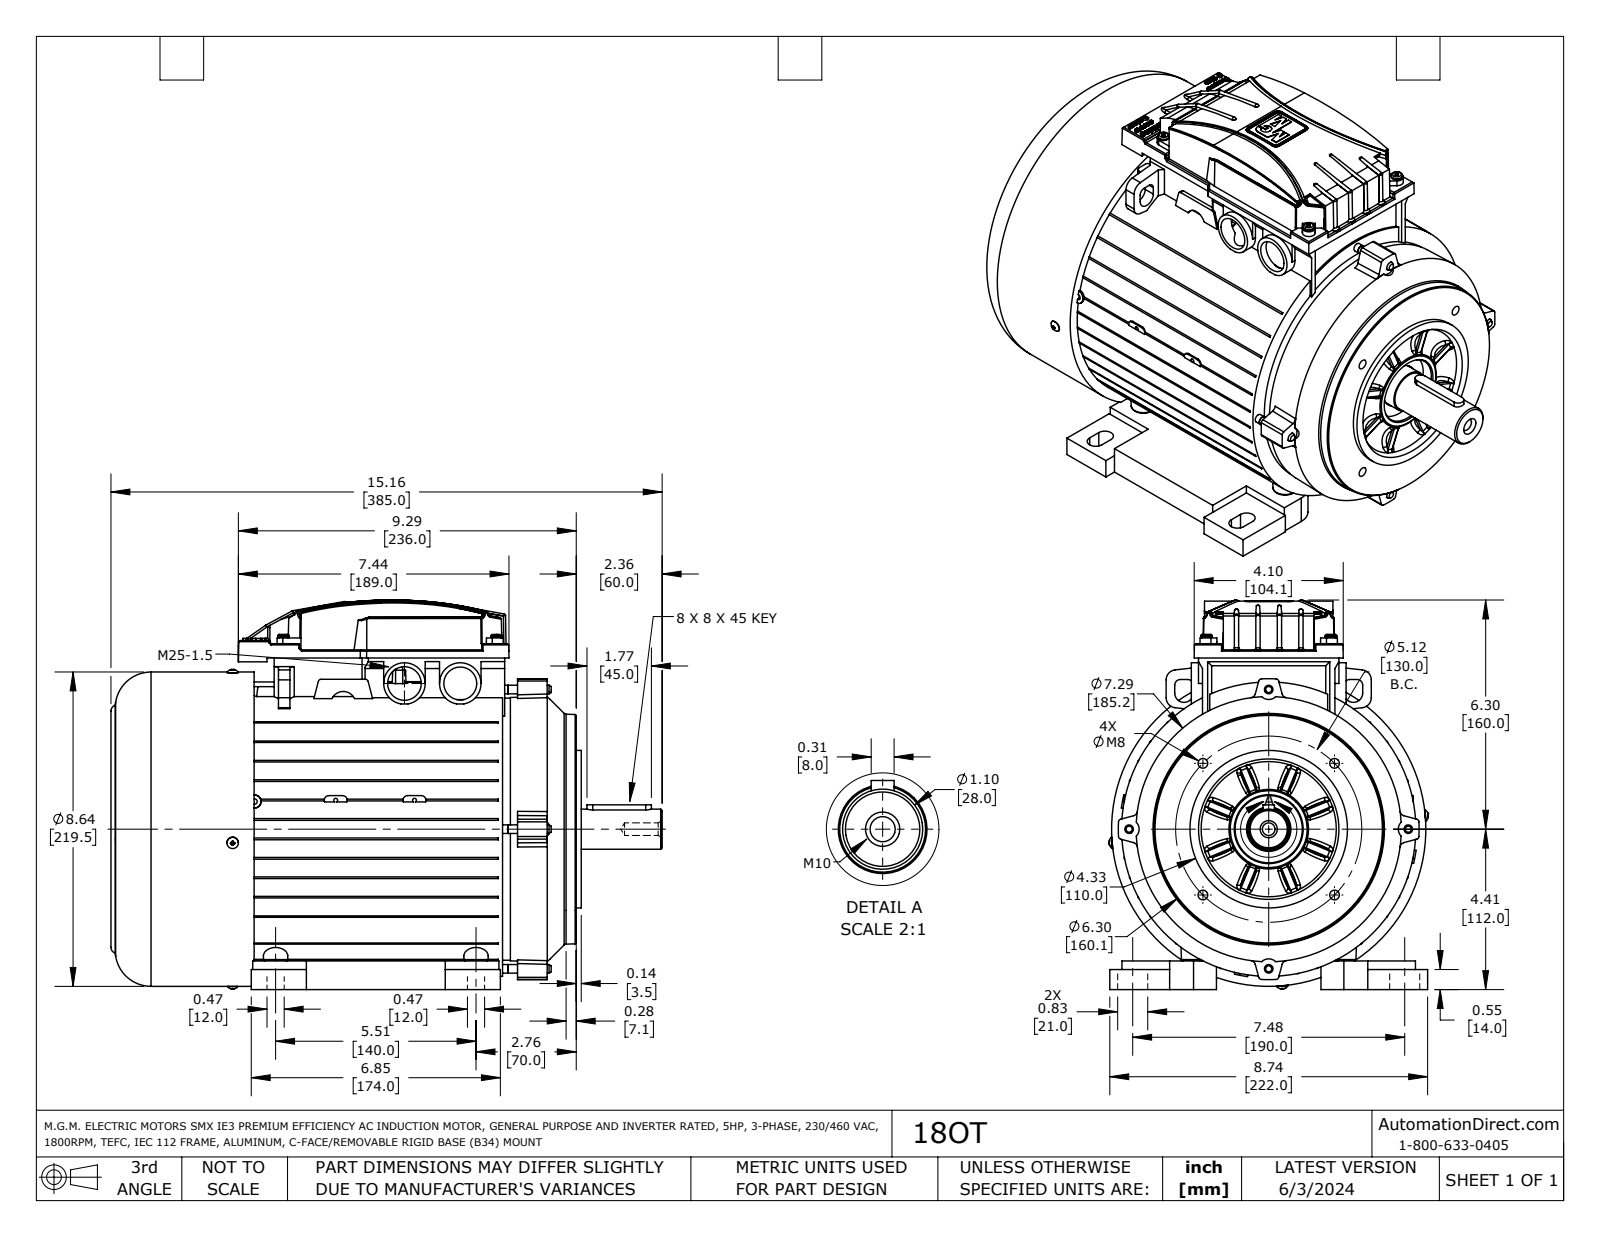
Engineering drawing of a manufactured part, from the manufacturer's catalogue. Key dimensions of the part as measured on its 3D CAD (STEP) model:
Part name (STEP PRODUCT): 18OT
STEP written by: SolidWorks 2021 (AUTOMOTIVE_DESIGN)
Units: inches
Bodies: 16 solids, 3525 faces (1703 planar, 684 cylindrical, 1138 other)
Overall size (bounding box): 15.157 × 10.709 × 8.78
Volume: 651.5 in³ · Surface area: 993.3 in²
Round holes (diameter × count): ⌀0.098 ×5, ⌀0.13 ×5, ⌀0.177 ×4, ⌀0.197 ×4, ⌀0.268 ×4, ⌀0.335 ×4, ⌀0.531 ×4, ⌀0.106 ×2, ⌀0.165 ×2, ⌀0.346 ×1, ⌀0.906 ×1, ⌀0.925 ×1
Round bosses / shafts (diameter × count): ⌀0.315 ×12, ⌀0.522 ×4, ⌀0.236 ×4, ⌀0.138 ×4, ⌀0.079 ×4, ⌀1.142 ×2, ⌀8.642 ×1, ⌀8.093 ×1
Partial cylindrical surfaces — rounded edges, fillets, slot ends (radius × count): R0.039 ×65, R0.008 ×56, R0.016 ×48, R0.059 ×45, R0.079 ×29, R0.004 ×24, R0.02 ×16, R0.033 ×16
Main face-to-face distances: 9.114, 0.787, 8.327, 1.811, 10.856, 12.667, 12.677, 10.866, 0.551, 0.236
Hole centre spacings: 2.719, 5.931, 2.559, 3.619, 3.839, 5.429, 0.611, 0.672
